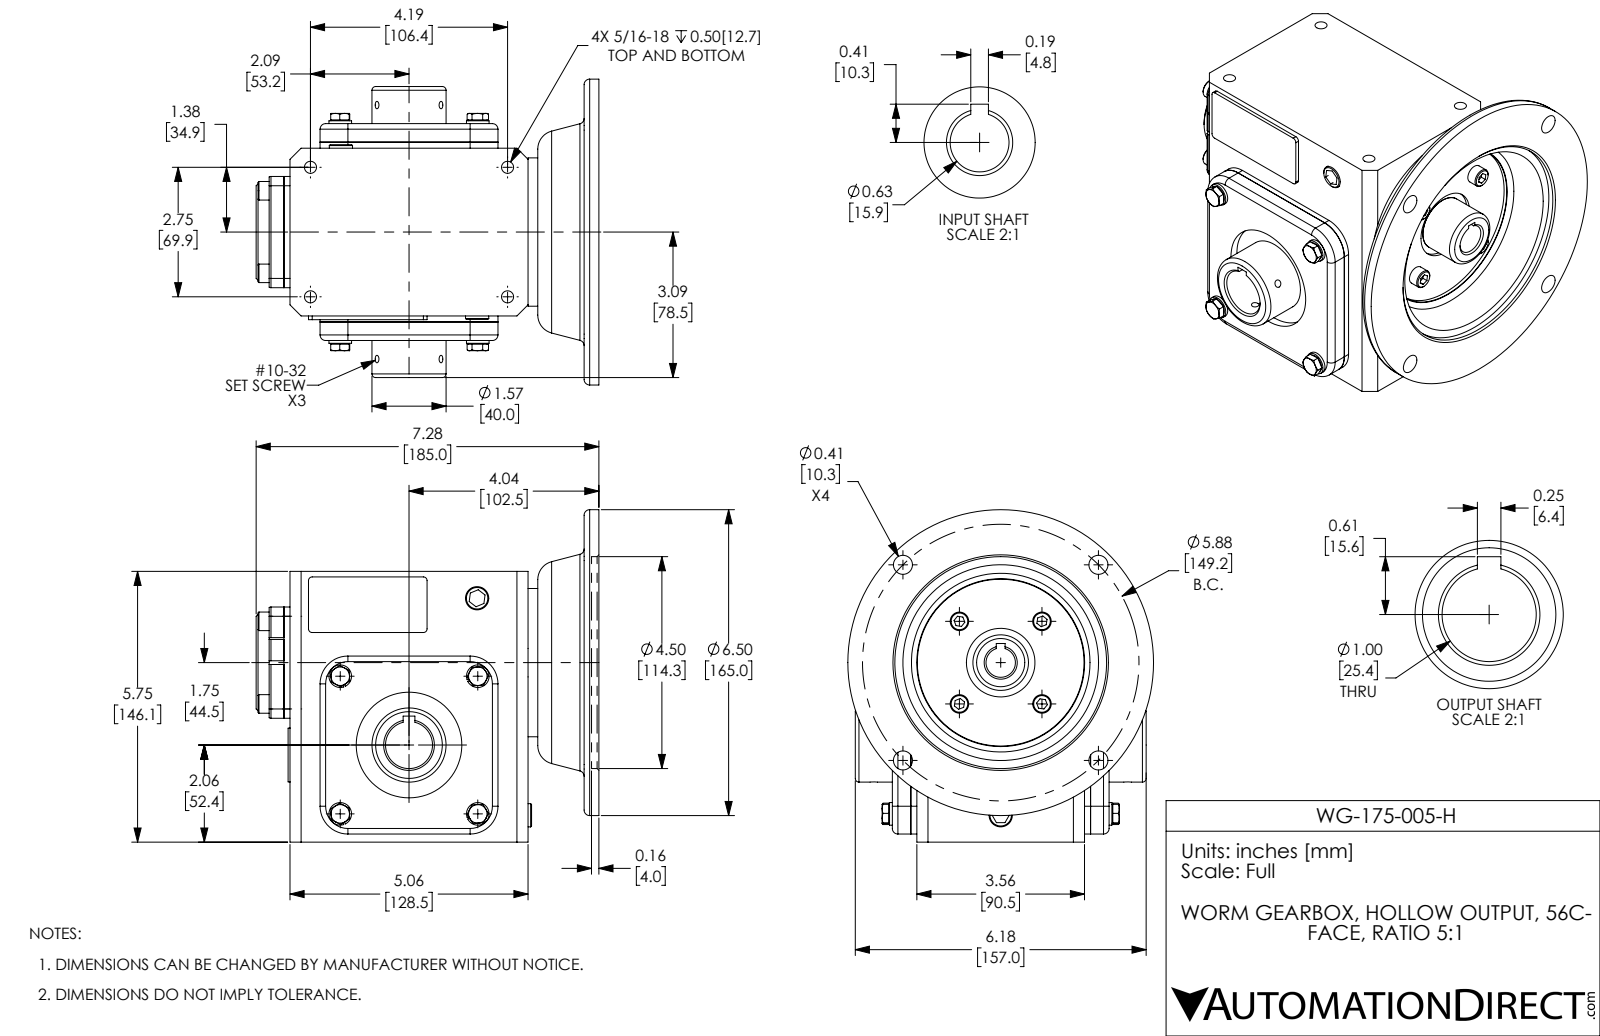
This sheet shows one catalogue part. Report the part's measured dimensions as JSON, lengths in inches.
{"part_name": "WG-175-005-H", "step_written_by": "SolidWorks 2015 (CONFIG_CONTROL_DESIGN)", "units": "inches", "bodies": {"solids": 44, "faces": 661, "planar": 339, "cylindrical": 194, "other": 128}, "overall_size": [7.283, 7.06, 6.496], "volume_in3": 131.1, "surface_area_in2": 382.7, "round_holes": [[0.159, 6], [0.257, 4], [0.406, 4], [0.591, 1], [0.625, 1], [1, 1], [1.457, 1], [1.575, 1], [2.244, 1], [3.543, 1], [4.5, 1]], "round_bosses_or_shafts": [[0.394, 8], [0.118, 5], [0.48, 4], [6.496, 1], [3.15, 1], [2.047, 1], [1.575, 1], [1.181, 1]], "partial_cylinders_radius": [[0.079, 8], [0.118, 8], [0.197, 4], [0.591, 4], [0.02, 2], [0.039, 2]], "face_to_face_distances": [0.128, 3.819, 3.691, 0.394, 0.522, 4.085, 4.213, 5.75, 0.315, 6.693], "hole_center_spacings": [2.476, 2.937, 4.154, 4.579, 5.394, 2.08, 2.75, 4.188]}
